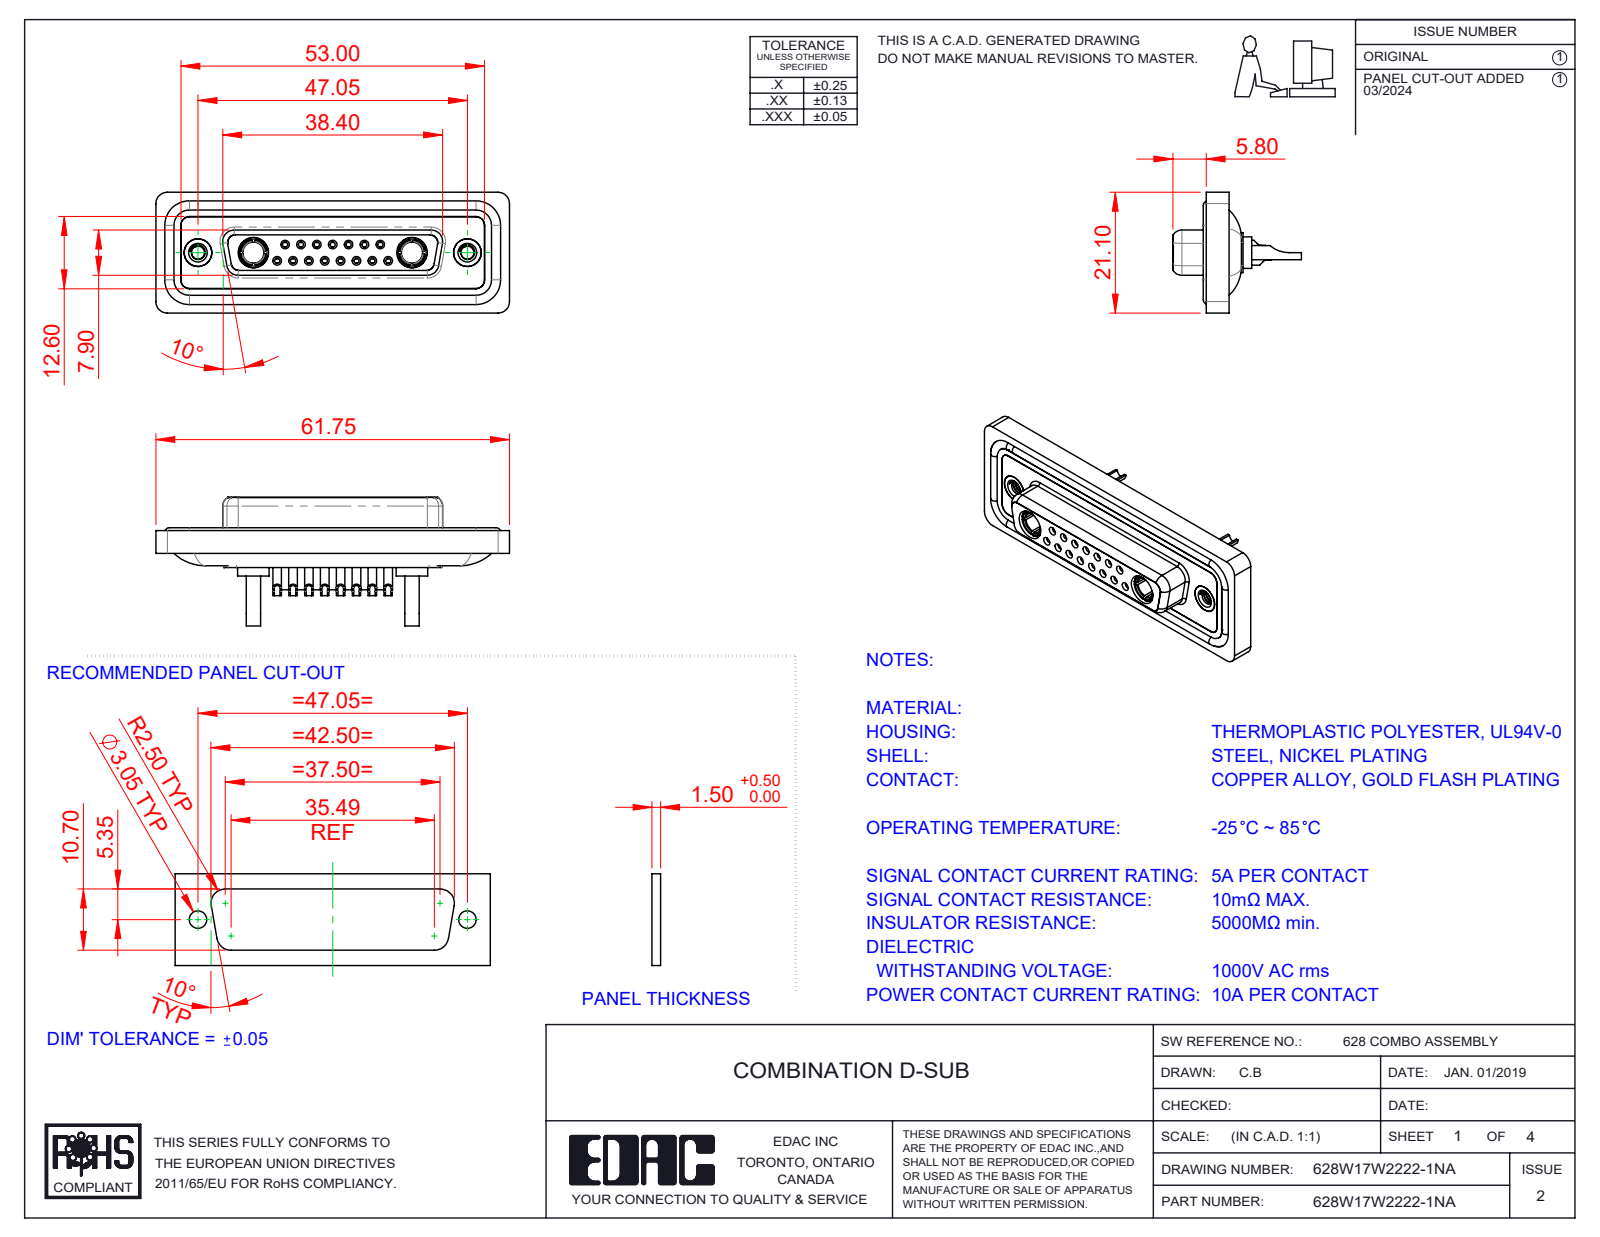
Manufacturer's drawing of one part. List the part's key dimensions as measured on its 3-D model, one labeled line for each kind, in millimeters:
Part name (STEP PRODUCT): 628Combo Contact Row 1_22; Power Socket_10A SC; 628Combo Housing_17W2; 628Combo Shell Front_25 Contacts (+5 more)
STEP written by: SolidWorks 2023 (CONFIG_CONTROL_DESIGN)
Units: millimetres
Bodies: 26 solids, 1367 faces (422 planar, 557 cylindrical, 388 other)
Overall size (bounding box): 61.75 × 22.45 × 21.1
Volume: 8 351 mm³ · Surface area: 14 108 mm²
Round holes (diameter × count): ⌀0.9 ×15, ⌀1 ×15, ⌀1.1 ×15, ⌀1.5 ×15, ⌀2 ×15, ⌀1.6 ×8, ⌀1.7 ×7, ⌀4.85 ×4, ⌀1.7 ×2, ⌀2.26 ×2, ⌀3.7 ×2, ⌀4 ×2
Round bosses / shafts (diameter × count): ⌀2.2 ×15, ⌀1.6 ×11, ⌀5.5 ×2, ⌀5.2 ×2, ⌀4.96 ×2, ⌀4.95 ×2, ⌀4.8 ×2, ⌀4.75 ×2
Partial cylindrical surfaces — rounded edges, fillets, slot ends (radius × count): R1.5 ×22, R2 ×18, R1.35 ×8, R1.6 ×8, R1 ×6, R0.25 ×4, R0.5 ×4, R0.6 ×4
Main face-to-face distances: 0.4, 1.8, 7.45, 5.65, 6.6, 0.5, 7.05, 1.6, 2.9, 1.1
Hole centre spacings: 3.16, 2.77, 8.31, 5.54, 5.03, 5.04, 7.49, 11.08
